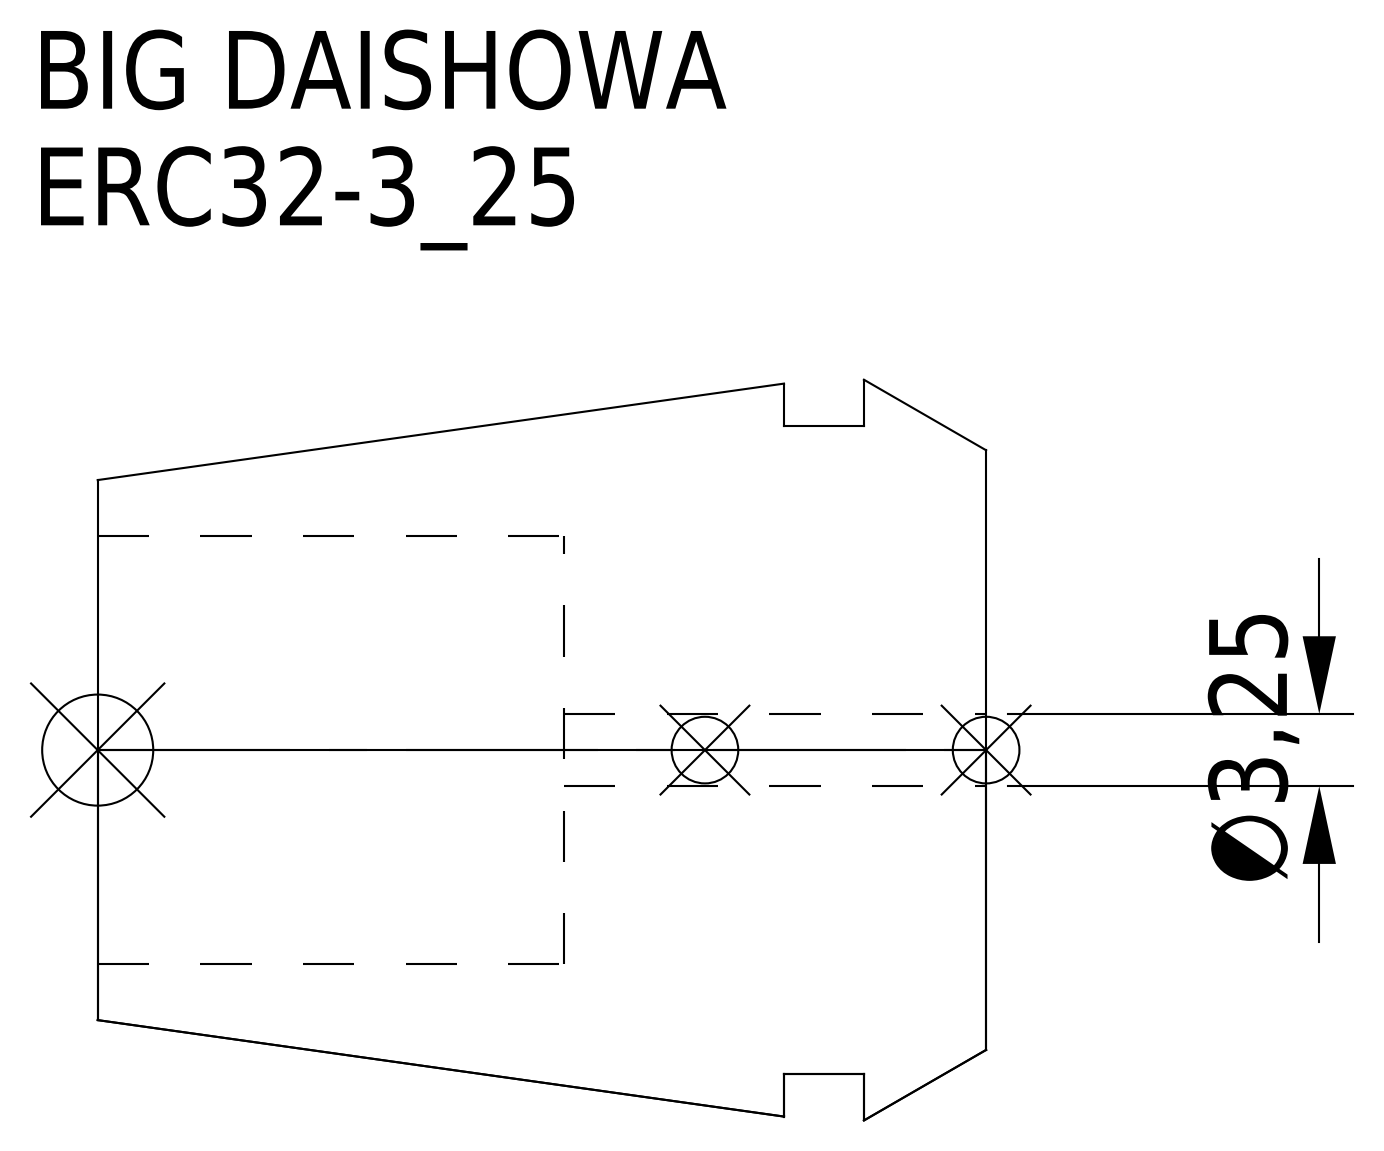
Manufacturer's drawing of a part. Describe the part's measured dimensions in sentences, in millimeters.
The part is named "ERC32-3_25". Its 3-D file was written by "CREO PARAMETRIC BY PTC INC, 2016380 (AUTOMOTIVE_DESIGN)". It is 1 solid with 15 faces: 5 planar, 6 cylindrical and 4 other. Overall it measures 40 by 33.35 by 33.35 millimeters. Its volume is 20 141 cubic millimeters and its surface area 6 619 square millimeters. Round holes: 1 of diameter 3.25, 1 of diameter 19.3. Round bosses or shafts: 1 of diameter 29.2. The main face-to-face distances are 19, 5.5, 13.5, 9.1, 3.6, 9.9, 40, 34.5, 30.9, 21.
